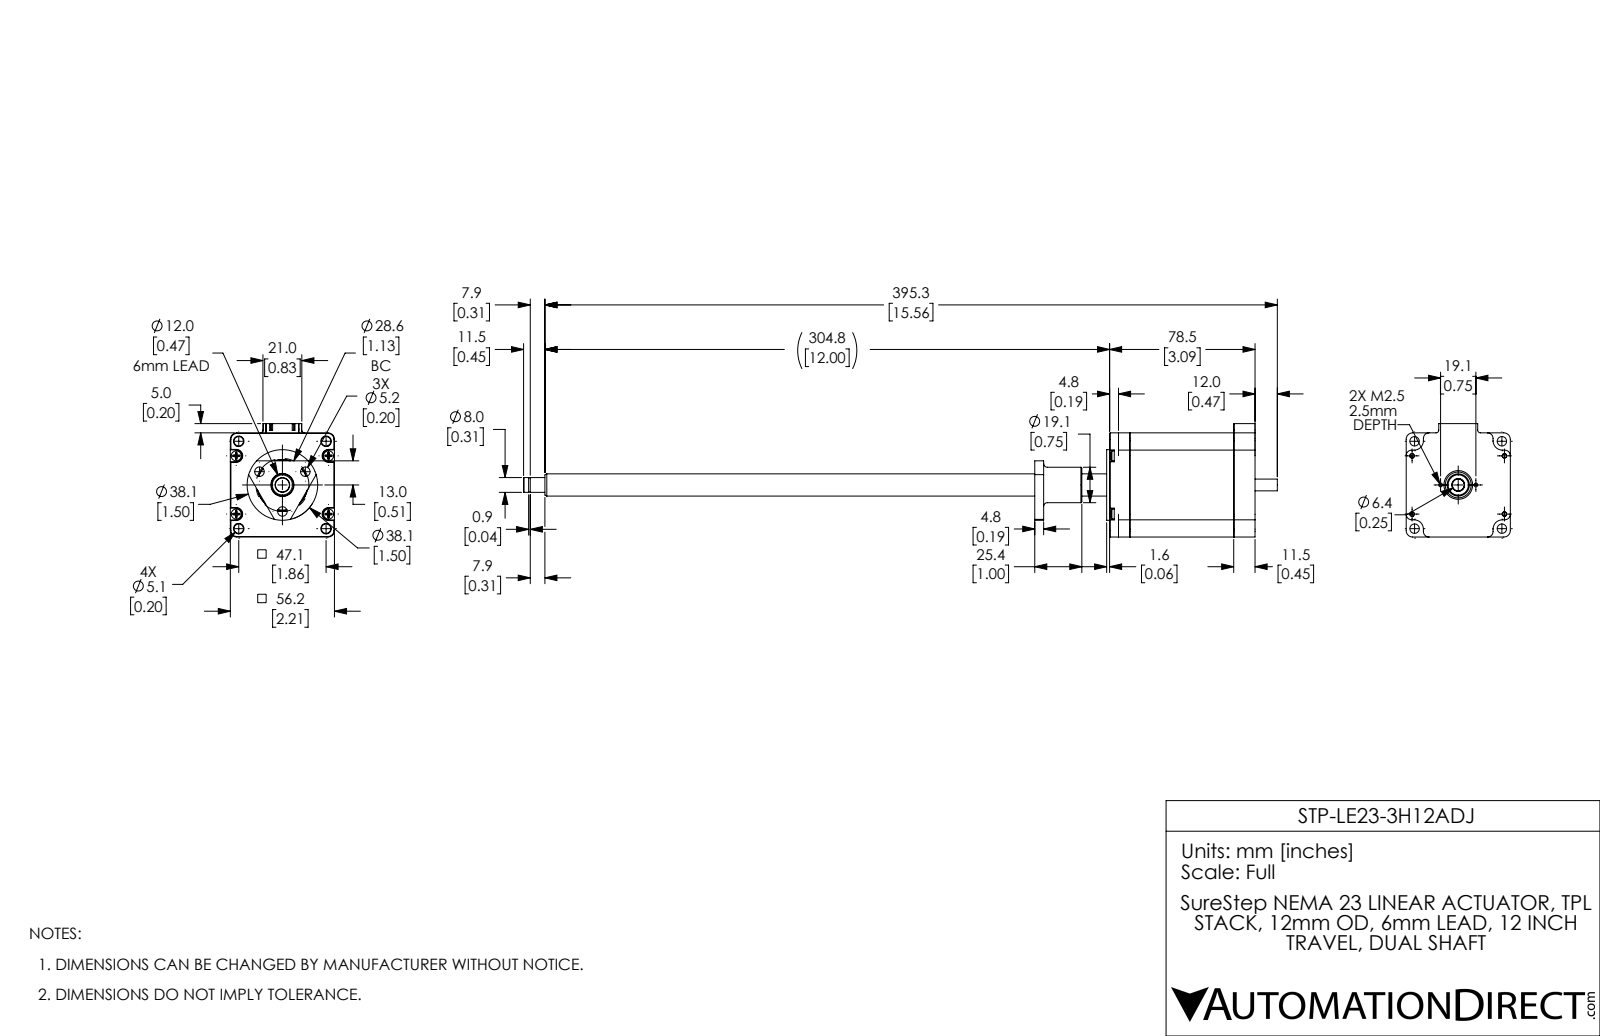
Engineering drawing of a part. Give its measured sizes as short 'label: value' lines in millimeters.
name: STP-LE23-3H12ADJ; STP-LE23-3H12ADJ_1; STP-LE23-3H12ADJ_2
written by: SolidWorks 2017 (AUTOMOTIVE_DESIGN)
unit: mm
bodies: 7 solids, 1001 faces (380 planar, 460 cylindrical, 161 other)
size: 406.8 × 61.2 × 56.2
volume: 243 097 mm³; area: 68 829 mm²
holes: 8× ⌀4.5, 4× ⌀2.5, 4× ⌀3.3, 4× ⌀5.1, 3× ⌀5.16, 2× ⌀2, 2× ⌀2.05, 1× ⌀6.9, 1× ⌀10.5, 1× ⌀14.8, 1× ⌀15.5, 1× ⌀16
bosses: 4× ⌀5.4, 4× ⌀2.91, 1× ⌀38.1, 1× ⌀36, 1× ⌀35.6, 1× ⌀34.85, 1× ⌀28, 1× ⌀19.1
rounds: 10× R1.5, 8× R0.2, 8× R3, 4× R1.8, 4× R3.2, 4× R3.5, 4× R5, 1× R0.6
face distances: 56.2, 56, 11.5, 67.5, 78.5, 11, 51.4, 67, 1.6, 1.1
hole spacings: 24.75, 14.12, 33.05, 35.01, 45.74, 48.53, 56.99, 6.55
